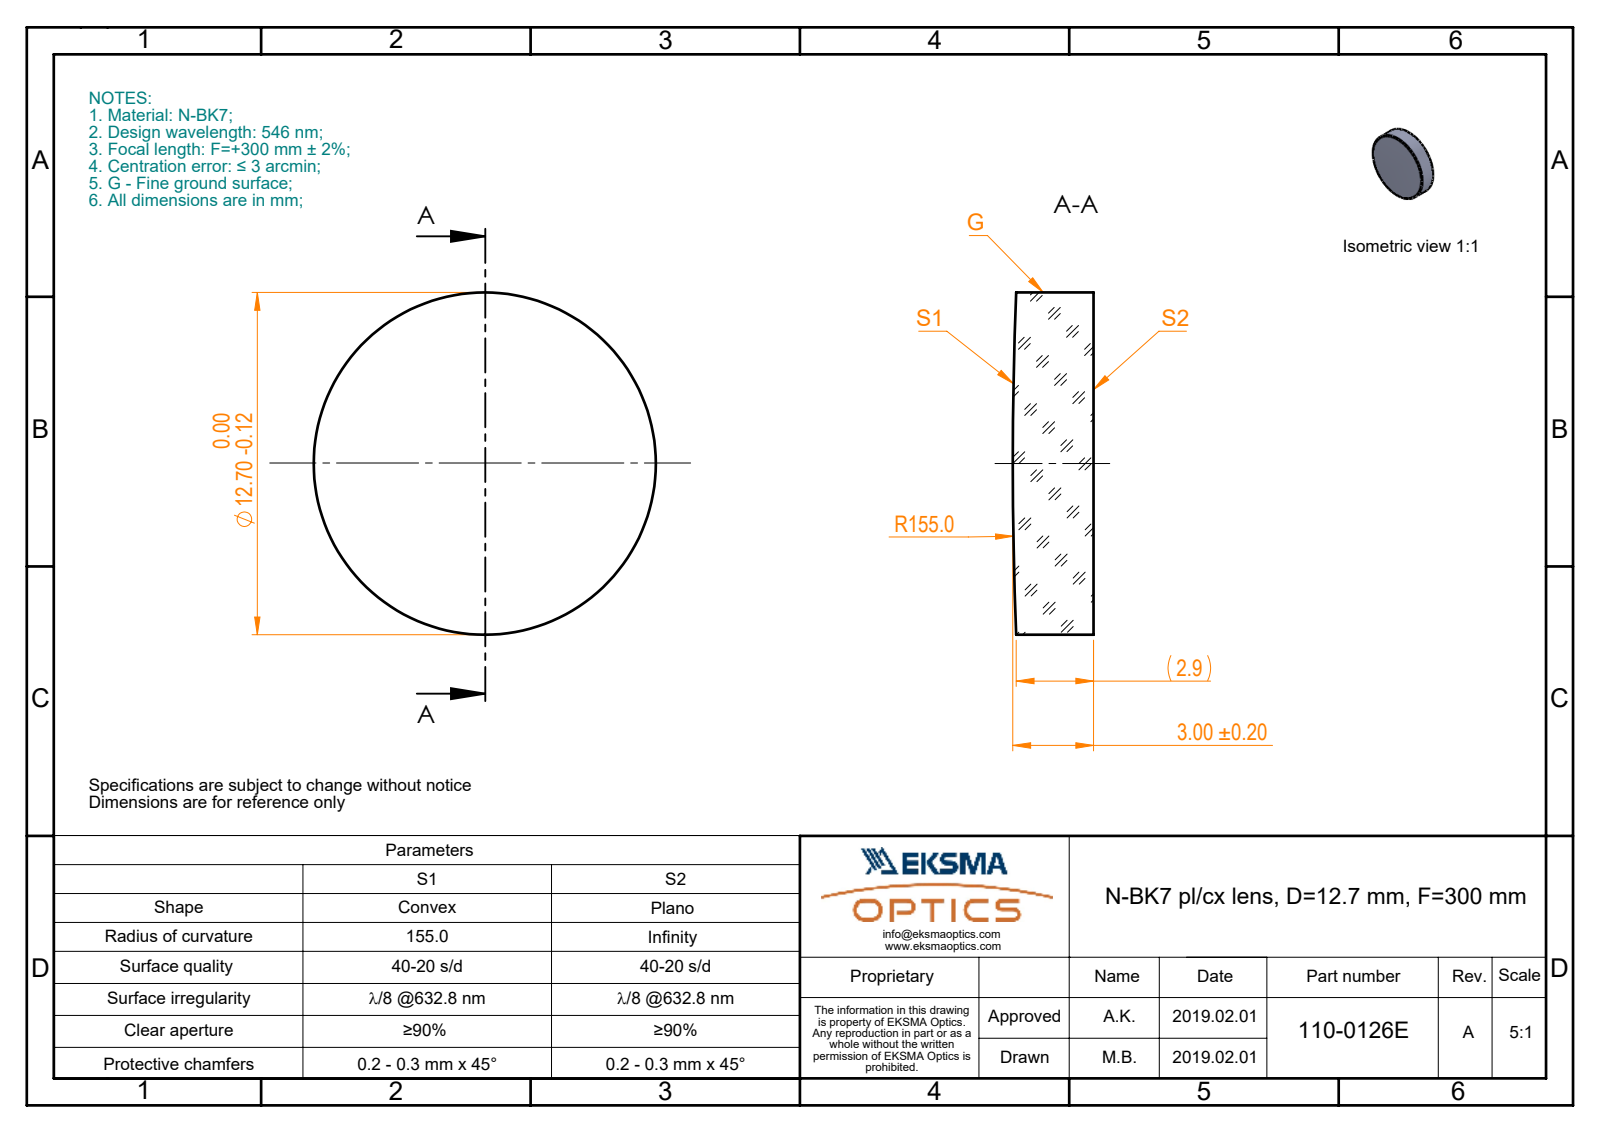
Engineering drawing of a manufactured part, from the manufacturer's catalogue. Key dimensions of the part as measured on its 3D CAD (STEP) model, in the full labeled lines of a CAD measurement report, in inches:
Part name (STEP PRODUCT): 110-0126E BK7 pl-cx 12.7 F300
STEP written by: SolidWorks 2017 (CONFIG_CONTROL_DESIGN)
Units: inches
Bodies: 1 solid, 5 faces (1 planar, 2 cylindrical, 2 other)
Overall size (bounding box): 0.5 × 0.5 × 0.118
Volume: 0.023 in³ · Surface area: 0.57 in²
Round bosses / shafts (diameter × count): ⌀0.5 ×1
